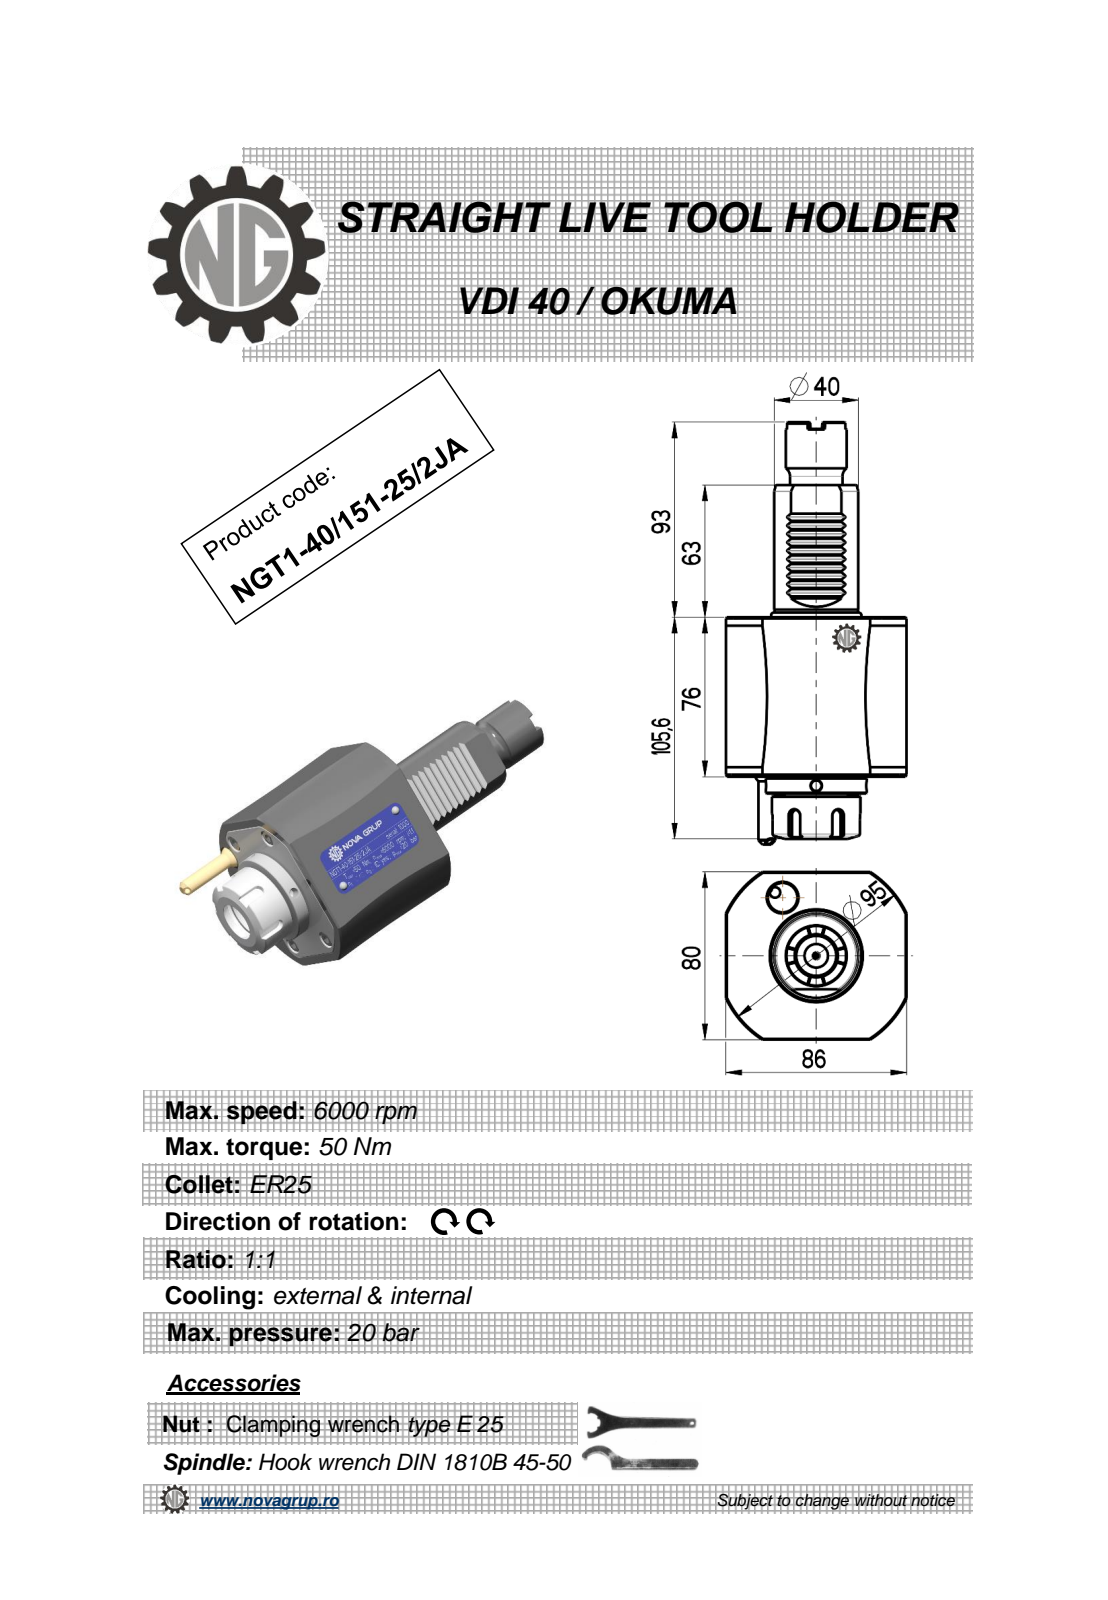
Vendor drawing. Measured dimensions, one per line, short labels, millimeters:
name: NGT1_40_151_25_1JA
written by: PRO/ENGINEER BY PARAMETRIC TECHNOLOGY CORPORATION, 2010280 (CONFIG_CONTROL_DESIGN)
unit: mm
bodies: 1 solid, 327 faces (116 planar, 68 cylindrical, 143 other)
size: 201.34 × 86 × 81.6
volume: 607 160 mm³; area: 54 071 mm²
holes: 3× ⌀5, 1× ⌀3, 1× ⌀20, 1× ⌀20.3
bosses: 1× ⌀48, 1× ⌀42, 1× ⌀41.5, 1× ⌀40, 1× ⌀33, 1× ⌀29, 1× ⌀25, 1× ⌀8
rounds: 10× R0.3, 6× R0.22, 5× R3, 1× R47.5
face distances: 76, 80, 86, 84, 8, 2.83, 5.66, 63, 139, 147
hole spacings: 40
